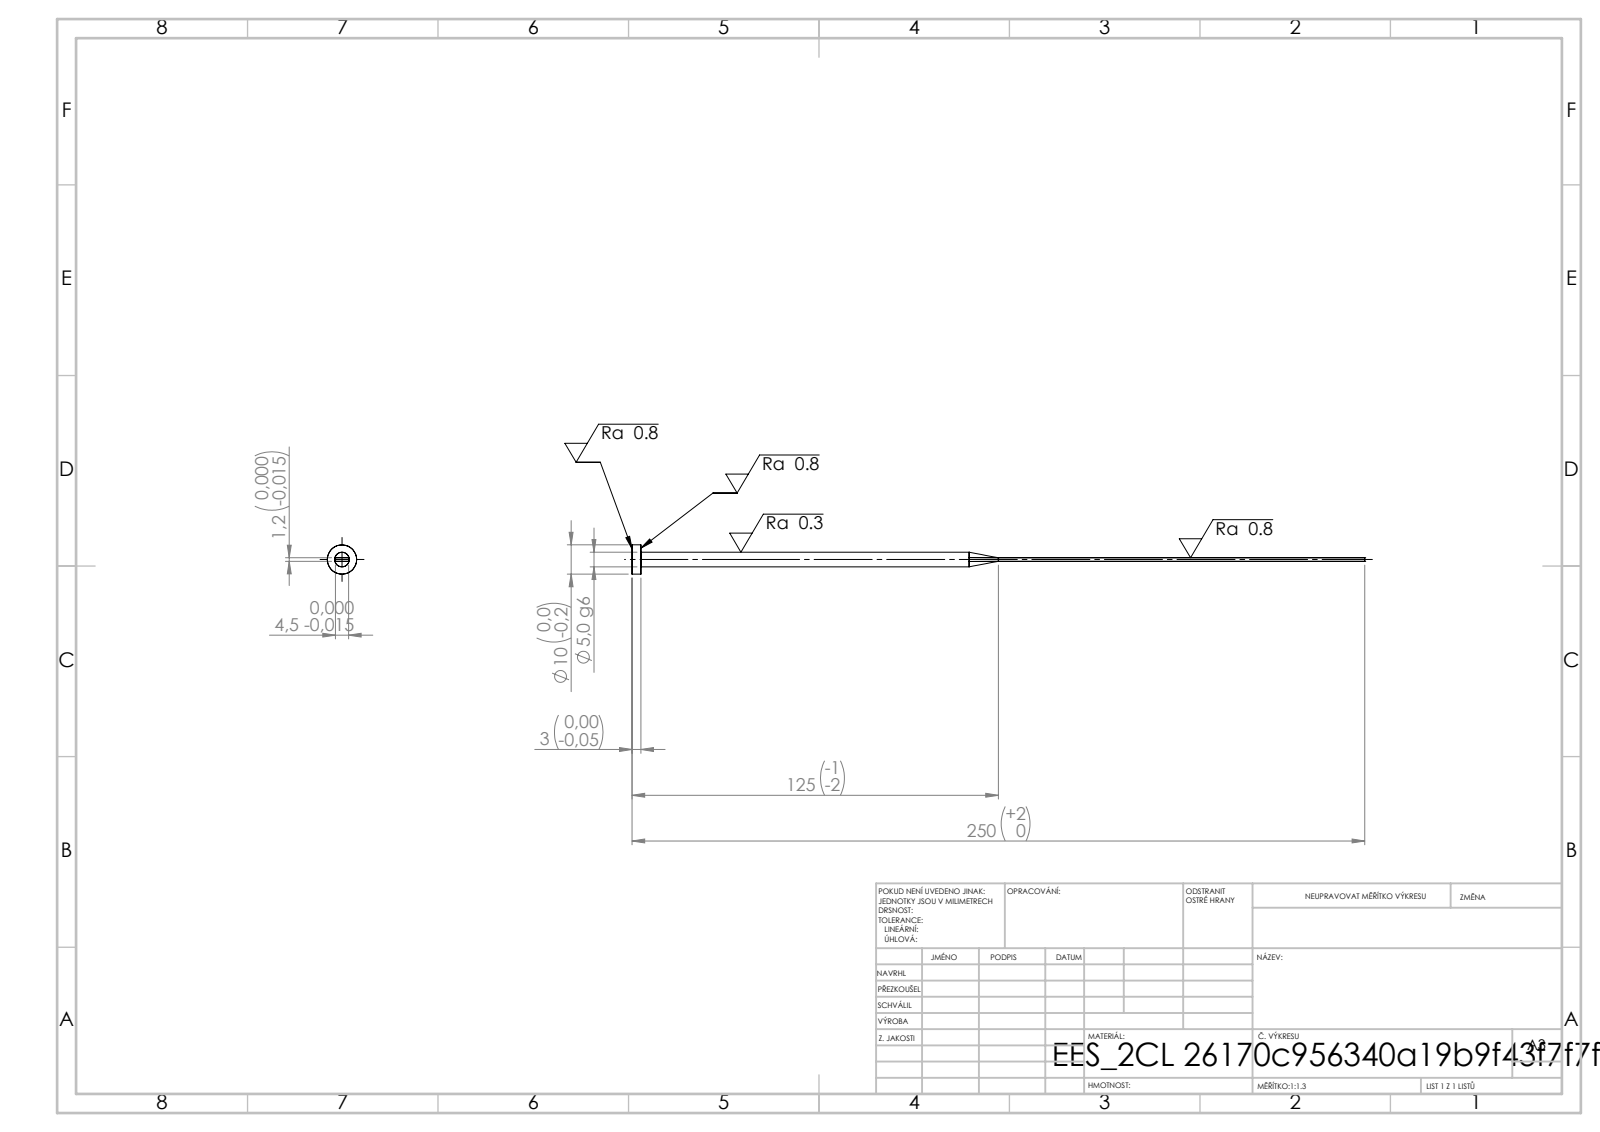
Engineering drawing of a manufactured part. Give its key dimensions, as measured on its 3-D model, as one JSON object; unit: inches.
{"step_written_by": "SolidWorks 2019 (CONFIG_CONTROL_DESIGN)", "units": "inches", "bodies": {"solids": 1, "faces": 15, "planar": 7, "cylindrical": 4, "other": 4}, "overall_size": [9.843, 0.394, 0.394], "volume_in3": 0.197, "surface_area_in2": 5.507, "round_bosses_or_shafts": [[0.394, 1], [0.197, 1]], "face_to_face_distances": [0.047, 0.177, 0.118, 9.843, 9.724]}
